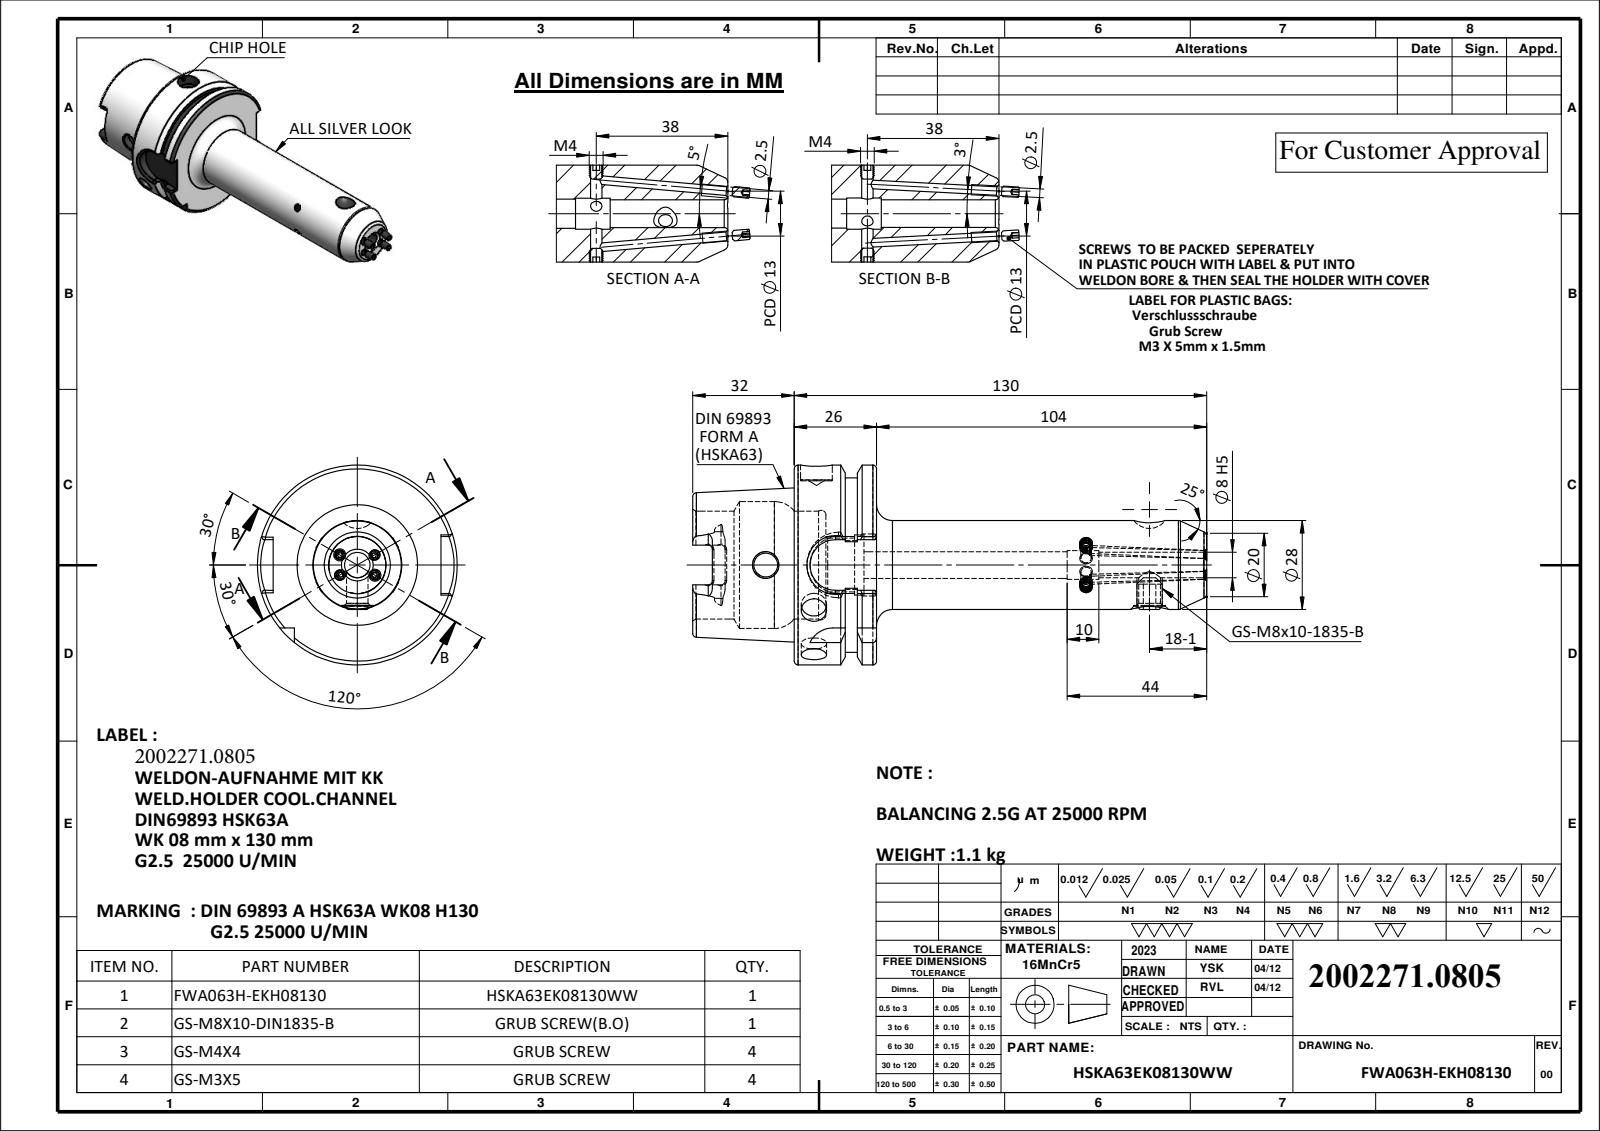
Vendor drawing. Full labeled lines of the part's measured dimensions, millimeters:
Part name (STEP PRODUCT): GS-M3X5; GS-M8X10-DIN1835-B; GS-M4X4_DIN 913 - M4 x 4-N; HSKA63EK08130WW (+1 more)
STEP written by: SolidWorks 2023 (CONFIG_CONTROL_DESIGN)
Units: millimetres
Bodies: 10 solids, 494 faces (153 planar, 121 cylindrical, 220 other)
Overall size (bounding box): 168.44 × 63 × 63
Volume: 137 369 mm³ · Surface area: 36 346 mm²
Round holes (diameter × count): ⌀2.5 ×4, ⌀8 ×3, ⌀3.3 ×2, ⌀10 ×2, ⌀6.8 ×1, ⌀7.5 ×1, ⌀8.4 ×1, ⌀9 ×1, ⌀17 ×1, ⌀19 ×1, ⌀34 ×1, ⌀40 ×1
Round bosses / shafts (diameter × count): ⌀3 ×4, ⌀4 ×2, ⌀63 ×1, ⌀55 ×1, ⌀28 ×1, ⌀8 ×1
Partial cylindrical surfaces — rounded edges, fillets, slot ends (radius × count): R1.3 ×6, R2.88 ×4, R8 ×2, R9 ×1
Main face-to-face distances: 25.95, 10, 15.95, 32, 42, 57.95, 52.9, 22, 12, 54
Hole centre spacings: 105
